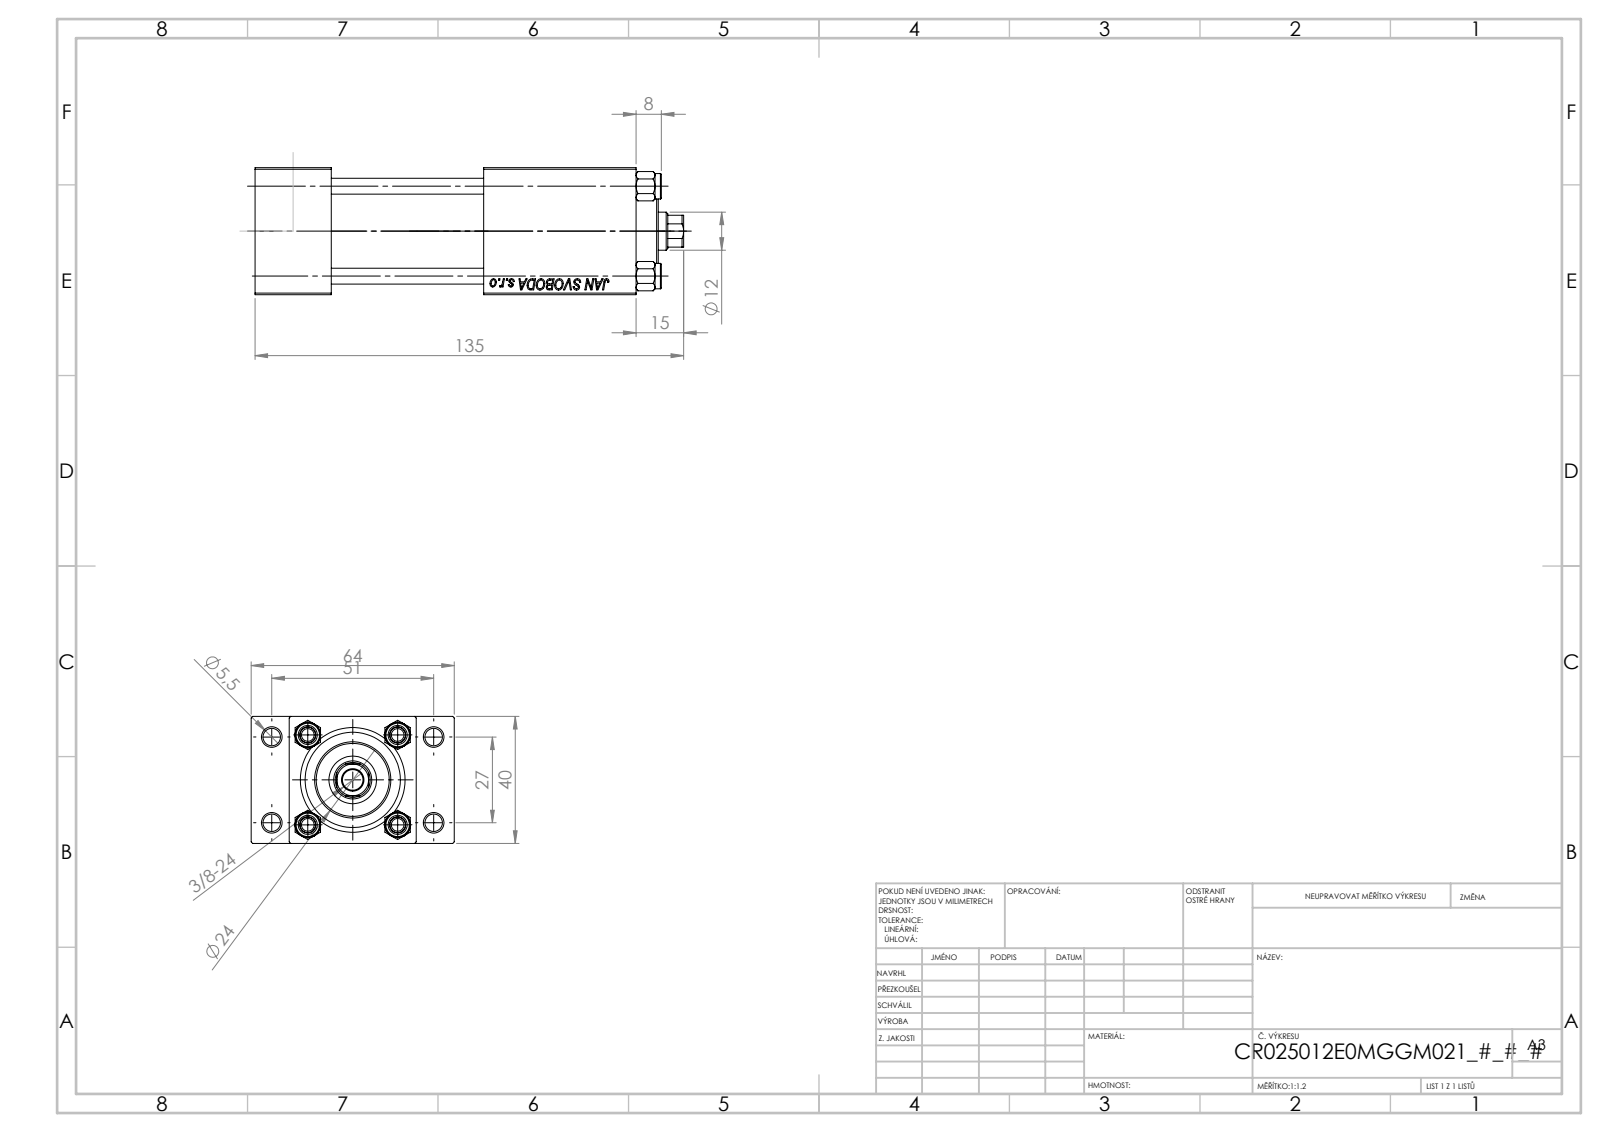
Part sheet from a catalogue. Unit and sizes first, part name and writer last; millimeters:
Units: millimetres
Overall size (bounding box): 135 × 64 × 40
Round holes (diameter × count): ⌀5 ×4, ⌀5.5 ×4, ⌀20 ×3, ⌀7 ×2, ⌀13.16 ×2, ⌀6.5 ×1, ⌀12 ×1, ⌀15 ×1, ⌀25 ×1, ⌀30 ×1
Round bosses / shafts (diameter × count): ⌀8 ×4, ⌀31 ×1, ⌀24 ×1
Partial cylindrical surfaces — rounded edges, fillets, slot ends (radius × count): R5.5 ×1
Main face-to-face distances: 40, 24, 12, 52, 48, 120, 96, 91.3, 67.3, 28.7
Hole centre spacings: 11.37, 20.01, 28.3, 28.85, 29.89, 39.66, 48.34, 27
Volume: 164 370 mm³ · Surface area: 62 381 mm²
Bodies: 11 solids, 1136 faces (497 planar, 87 cylindrical, 552 other)
Part name (STEP PRODUCT): V215_VC_A; NUT_M5_E; V215CR_TYCINKA_E; V215CR_E_Body (+1 more)
STEP written by: SolidWorks 2019 (CONFIG_CONTROL_DESIGN)
